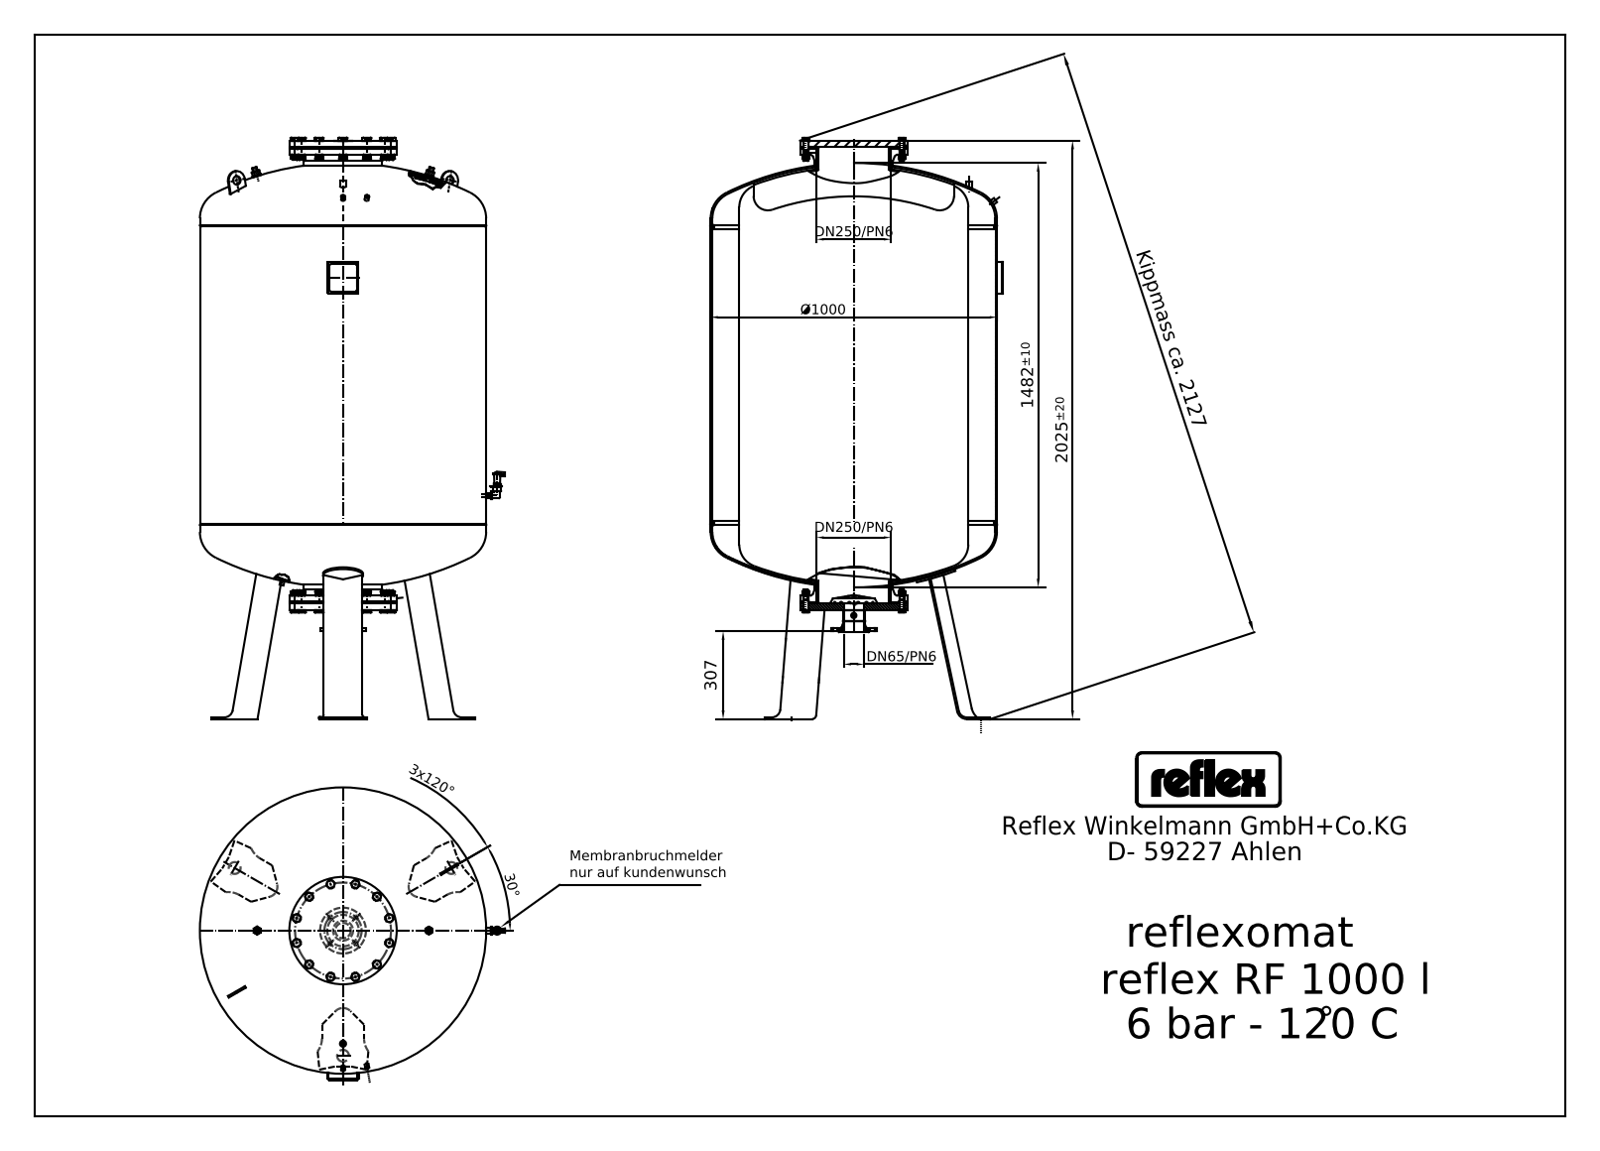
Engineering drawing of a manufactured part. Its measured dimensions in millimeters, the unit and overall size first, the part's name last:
Units: millimetres
Overall size (bounding box): 2030 × 1066 × 1020
Round holes (diameter × count): ⌀11.45 ×2, ⌀3.5 ×1, ⌀14.95 ×1, ⌀30 ×1, ⌀260.4 ×1
Round bosses / shafts (diameter × count): ⌀16 ×12, ⌀21.3 ×3, ⌀18.5 ×3, ⌀28 ×2, ⌀20 ×2, ⌀1000 ×1, ⌀375 ×1, ⌀273 ×1
Partial cylindrical surfaces — rounded edges, fillets, slot ends (radius × count): R25 ×18, R1 ×5, R8.44 ×4, R3.38 ×3, R6 ×3, R9 ×3, R2 ×2, R3 ×2
Main face-to-face distances: 1045, 22, 1615, 27, 1588, 1320.5, 275.5, 1342.5, 297.5, 294.5
Hole centre spacings: 395, 519.5, 652.61
Volume: 1 068 000 000 mm³ · Surface area: 10 560 000 mm²
Bodies: 23 solids, 940 faces (556 planar, 222 cylindrical, 162 other)
STEP written by: Mechanical Desktop 2009 (CONFIG_CONTROL_DESIGN)
